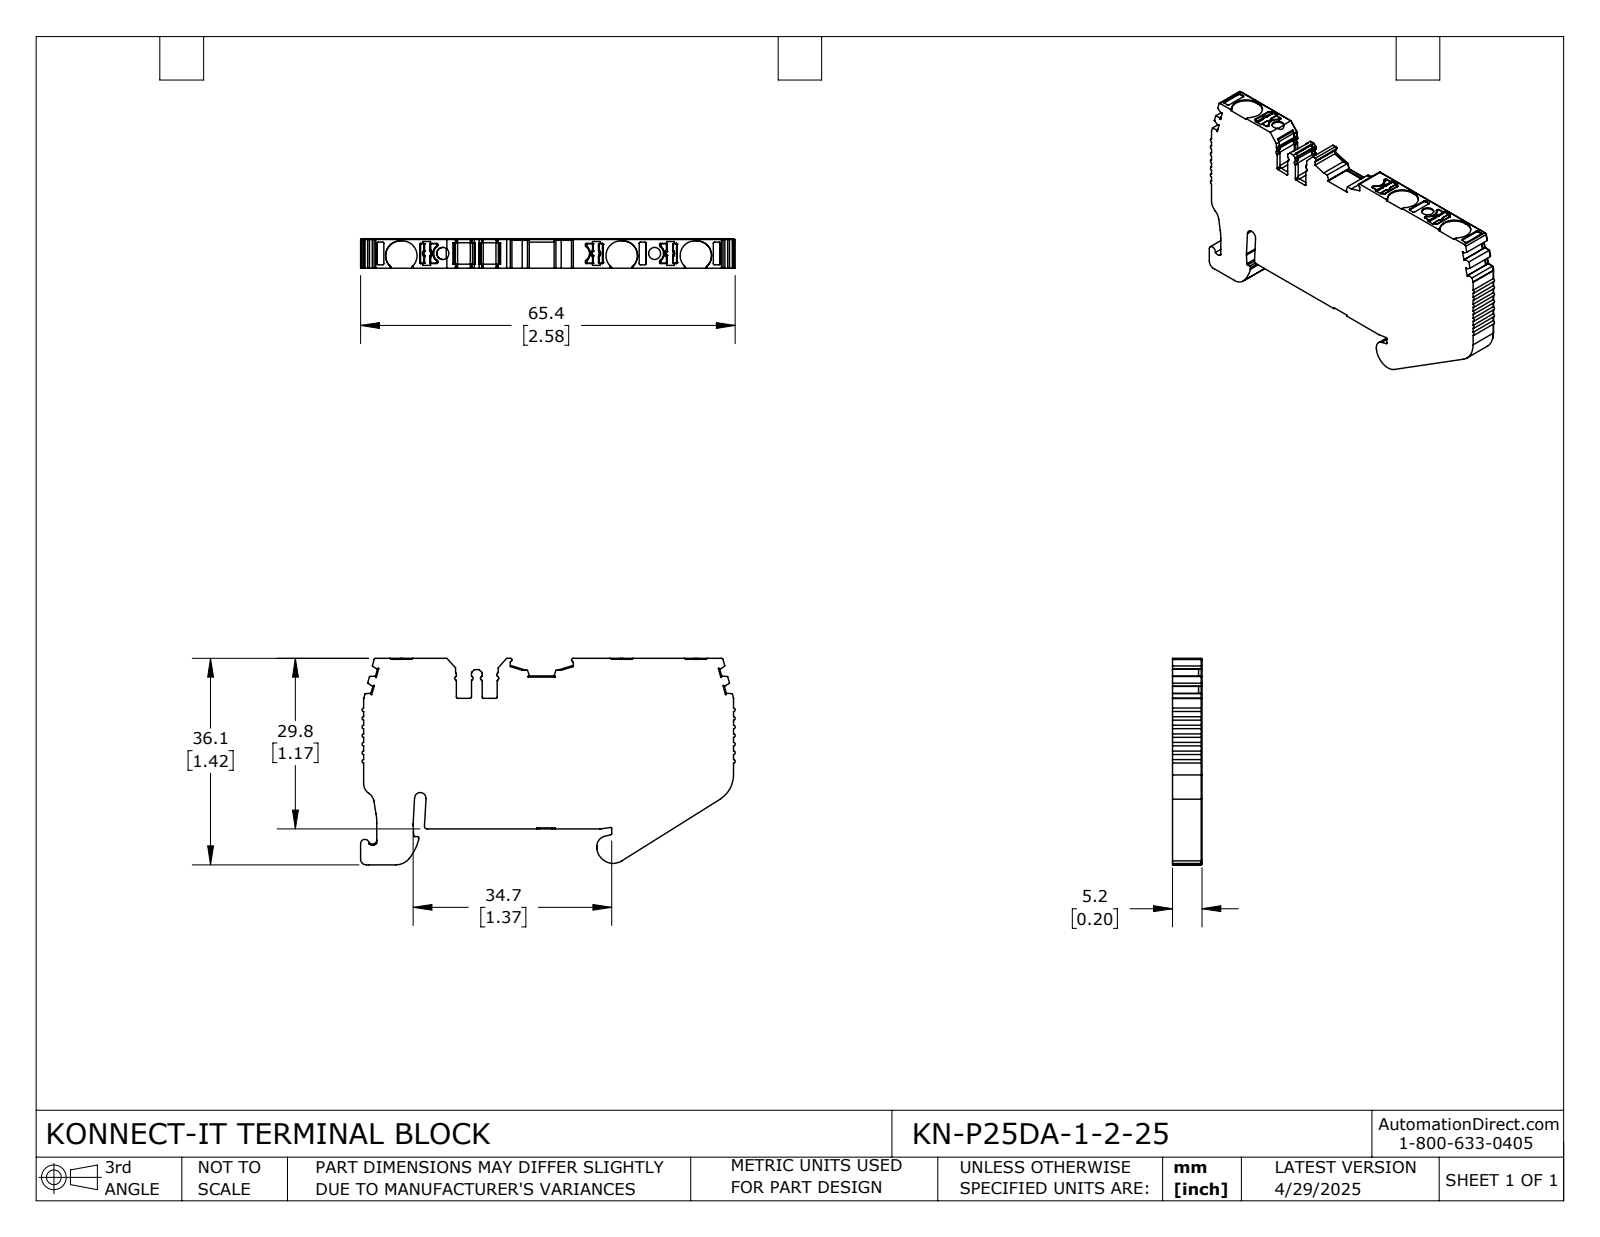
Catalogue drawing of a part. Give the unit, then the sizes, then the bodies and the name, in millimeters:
Units: millimetres
Overall size (bounding box): 65.42 × 36.07 × 5.15
Round holes (diameter × count): ⌀2.1 ×2
Partial cylindrical surfaces — rounded edges, fillets, slot ends (radius × count): R0.2 ×66, R0.3 ×39, R0.1 ×19, R0.5 ×18, R0.15 ×12, R0.4 ×9, R2.55 ×6, R1 ×3
Main face-to-face distances: 5.15, 29.61, 29.81, 64.58, 4.5, 5, 6.26, 35.87, 2, 36.07
Hole centre spacings: 36.98
Volume: 9 576 mm³ · Surface area: 5 140 mm²
Bodies: 1 solid, 655 faces (345 planar, 259 cylindrical, 51 other)
Part name (STEP PRODUCT): KN-P25DA-1-2-25
STEP written by: SolidWorks 2024 (CONFIG_CONTROL_DESIGN)
